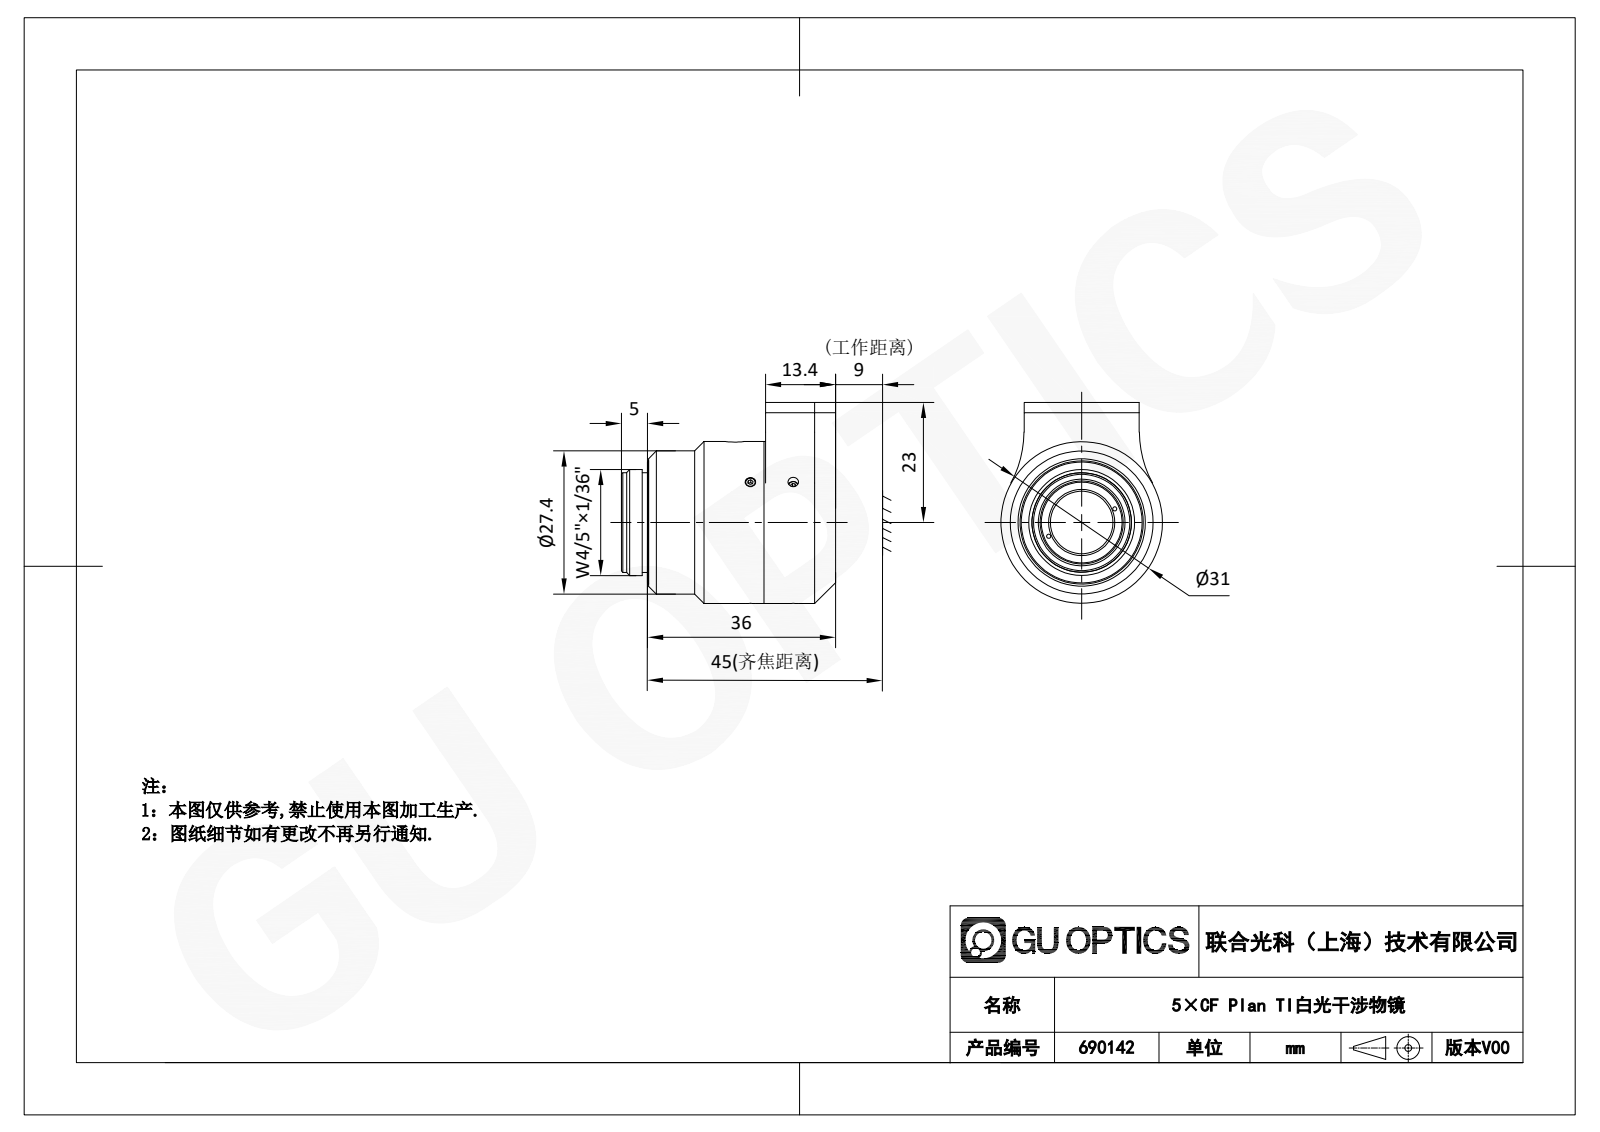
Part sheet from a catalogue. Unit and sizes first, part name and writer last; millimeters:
Units: millimetres
Overall size (bounding box): 41 × 38.5 × 31
Round holes (diameter × count): ⌀1.5 ×6, ⌀2 ×6, ⌀1.6 ×5, ⌀2.6 ×3, ⌀3.2 ×3, ⌀4 ×3, ⌀0.8 ×2, ⌀1.8 ×1, ⌀3 ×1, ⌀8 ×1, ⌀9.2 ×1, ⌀12 ×1
Round bosses / shafts (diameter × count): ⌀2.66 ×5, ⌀1.6 ×3, ⌀31 ×1, ⌀27.5 ×1, ⌀27.4 ×1, ⌀24.1 ×1, ⌀20.32 ×1, ⌀19.1 ×1
Partial cylindrical surfaces — rounded edges, fillets, slot ends (radius × count): R0.2 ×20, R0.3 ×12, R20 ×2, R5.5 ×1, R7.5 ×1
Main face-to-face distances: 2, 9.5, 13.3, 13.69, 4, 16.79, 10.2, 7.5, 10, 13.4
Hole centre spacings: 5.62, 6.72, 9.5, 13.37, 4.5, 8.2, 2.65, 2.98
Volume: 19 163 mm³ · Surface area: 19 059 mm²
Bodies: 26 solids, 504 faces (280 planar, 136 cylindrical, 88 other)
Part name (STEP PRODUCT): M2_____M2x5.STEP.STEP_1; O________23.6x1.8__A____.STEP.STEP_1; 5X______-2.STEP.STEP_1; .STEP.STEP_1 (+6 more)
STEP written by: SolidWorks 2020 (CONFIG_CONTROL_DESIGN)
